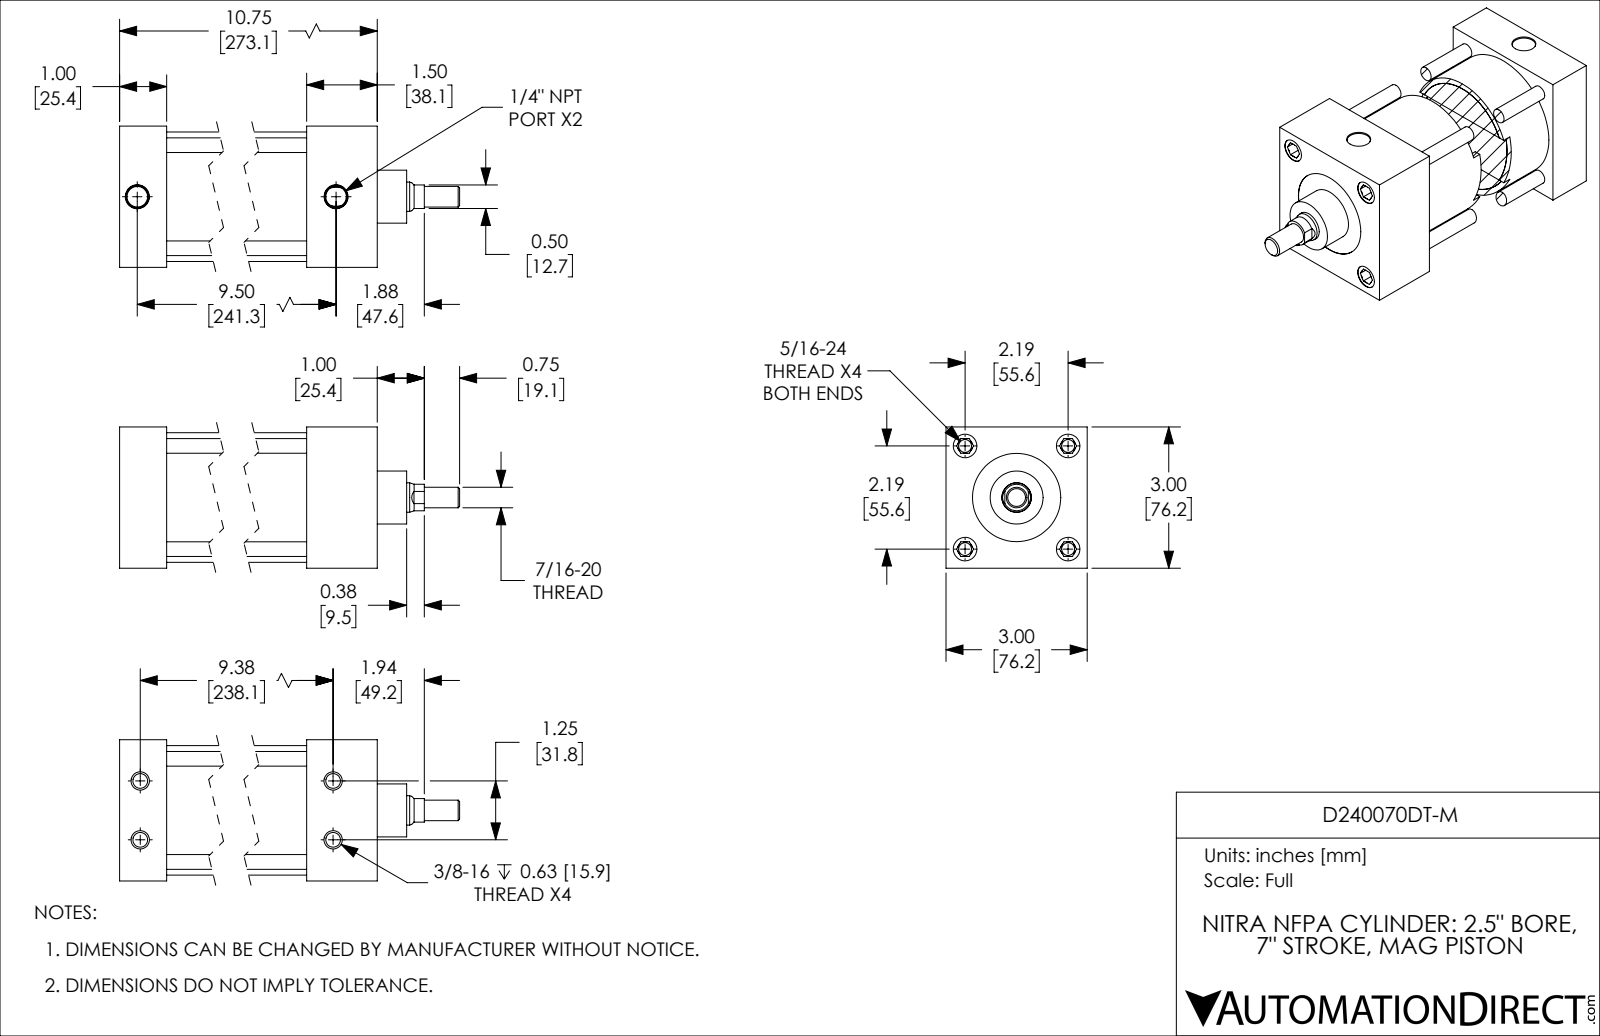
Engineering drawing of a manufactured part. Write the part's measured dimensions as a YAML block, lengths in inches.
part_name: "D240070DT-M; D240070DT-M_BODY; D240070DT-M_PISTON_KK1"
step_written_by: "SolidWorks 2019 (CONFIG_CONTROL_DESIGN)"
units: inches
bodies: {solids: 2, faces: 200, planar: 58, cylindrical: 62, other: 80}
overall_size: [12.5, 3, 3]
volume: 41.53
surface_area: 288.8
round_holes:
  - {diameter: 0.272, count: 4}
  - {diameter: 0.313, count: 4}
  - {diameter: 0.5, count: 4}
  - {diameter: 0.438, count: 2}
  - {diameter: 0.626, count: 1}
  - {diameter: 1.875, count: 1}
  - {diameter: 2.501, count: 1}
round_bosses_or_shafts:
  - {diameter: 0.312, count: 4}
  - {diameter: 2.751, count: 1}
  - {diameter: 2.499, count: 1}
  - {diameter: 1.125, count: 1}
  - {diameter: 0.624, count: 1}
  - {diameter: 0.437, count: 1}
partial_cylinders:
  - {radius: 0.281, count: 1}
face_to_face_distances: [3, 1, 9.25, 8.25, 10.75, 9.75, 1.5, 1.25, 2.25, 7]
hole_center_spacings: [1.548, 2.19, 9.458, 0.628, 0.628, 1.25, 3.097, 9.375]
